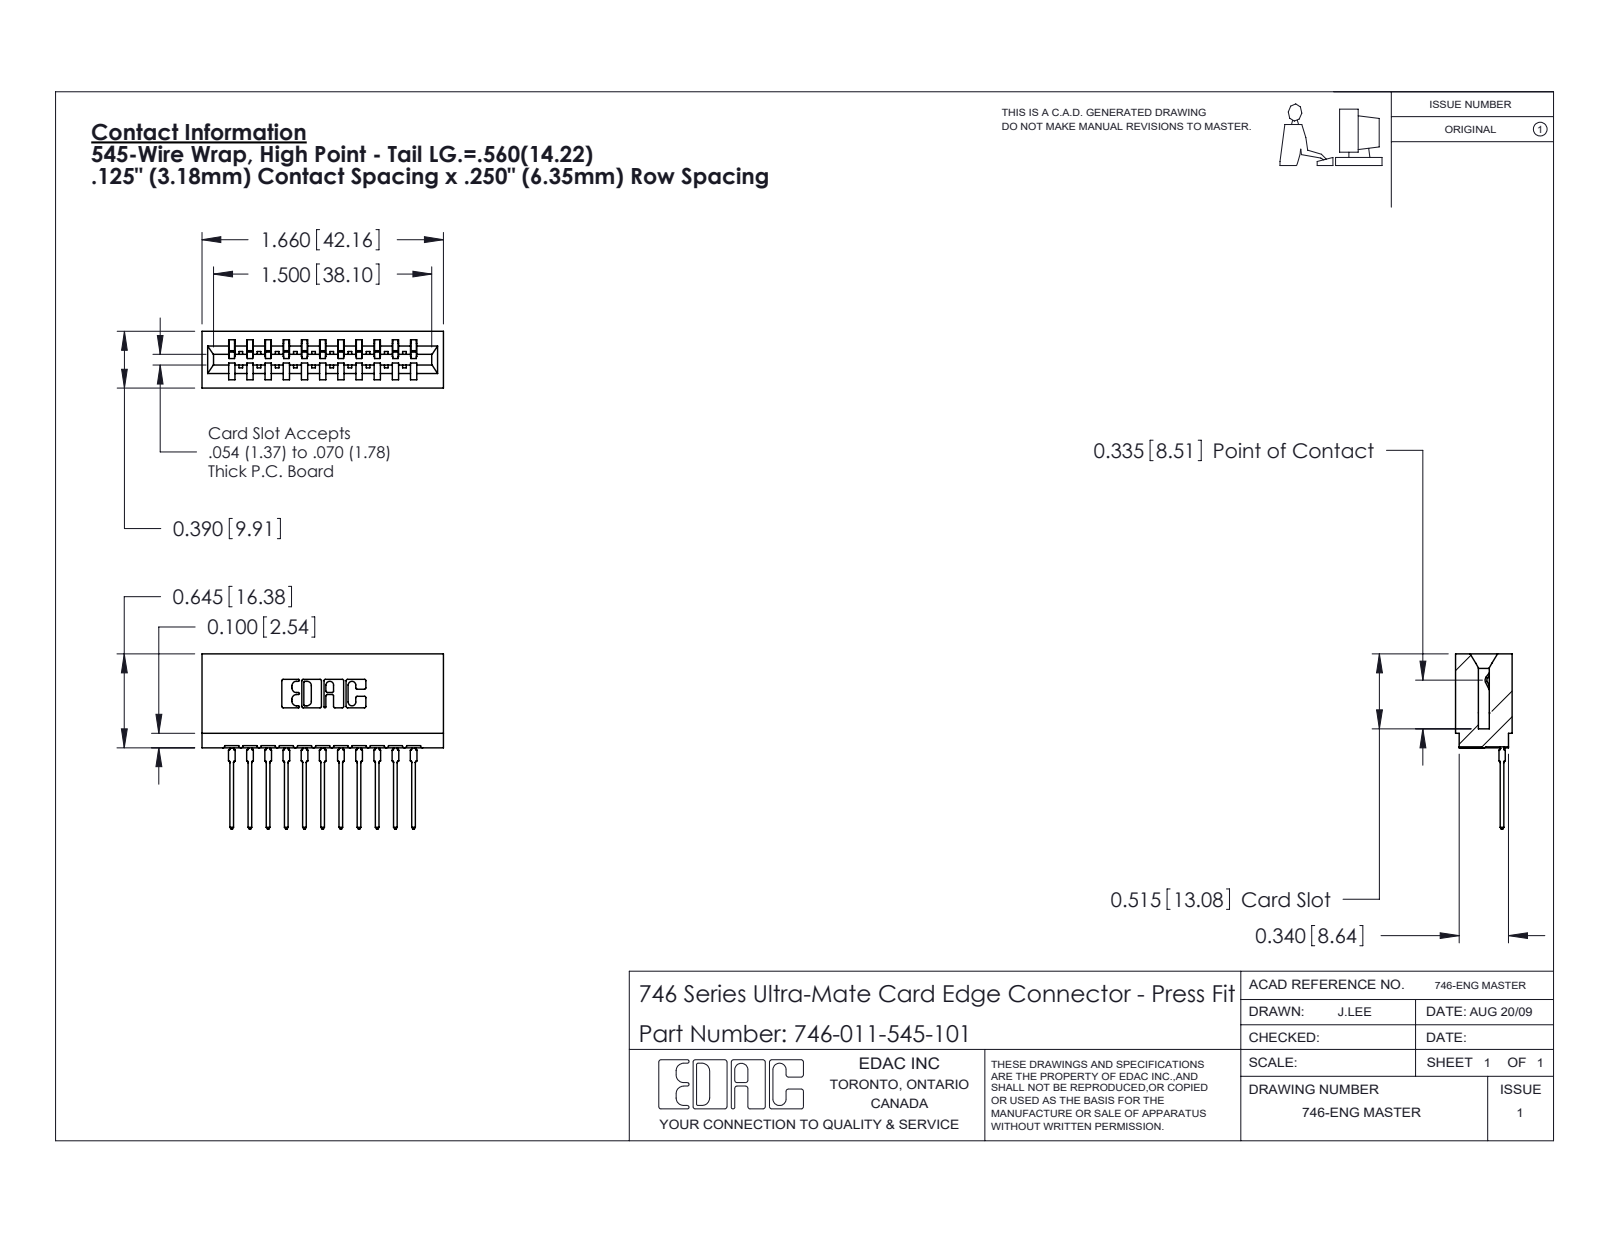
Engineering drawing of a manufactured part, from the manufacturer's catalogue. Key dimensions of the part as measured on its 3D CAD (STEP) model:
Part name (STEP PRODUCT): 746-292-001_545; 746-011-545-101; 746 Part_.515 Slot Depth - 01
STEP written by: SolidWorks 2020 (CONFIG_CONTROL_DESIGN)
Units: inches
Bodies: 12 solids, 1285 faces (748 planar, 251 cylindrical, 286 other)
Overall size (bounding box): 1.66 × 1.204 × 0.39
Volume: 0.284 in³ · Surface area: 10.11 in²
Partial cylindrical surfaces — rounded edges, fillets, slot ends (radius × count): R0.01 ×22, R0.021 ×22, R0.015 ×12, R0.007 ×6, R0.031 ×6, R0.005 ×4, R0.011 ×4, R0.026 ×3
Main face-to-face distances: 0.25, 0.333, 0.5, 0.057, 0.125, 0.125, 0.39, 0.042, 0.208, 0.083
